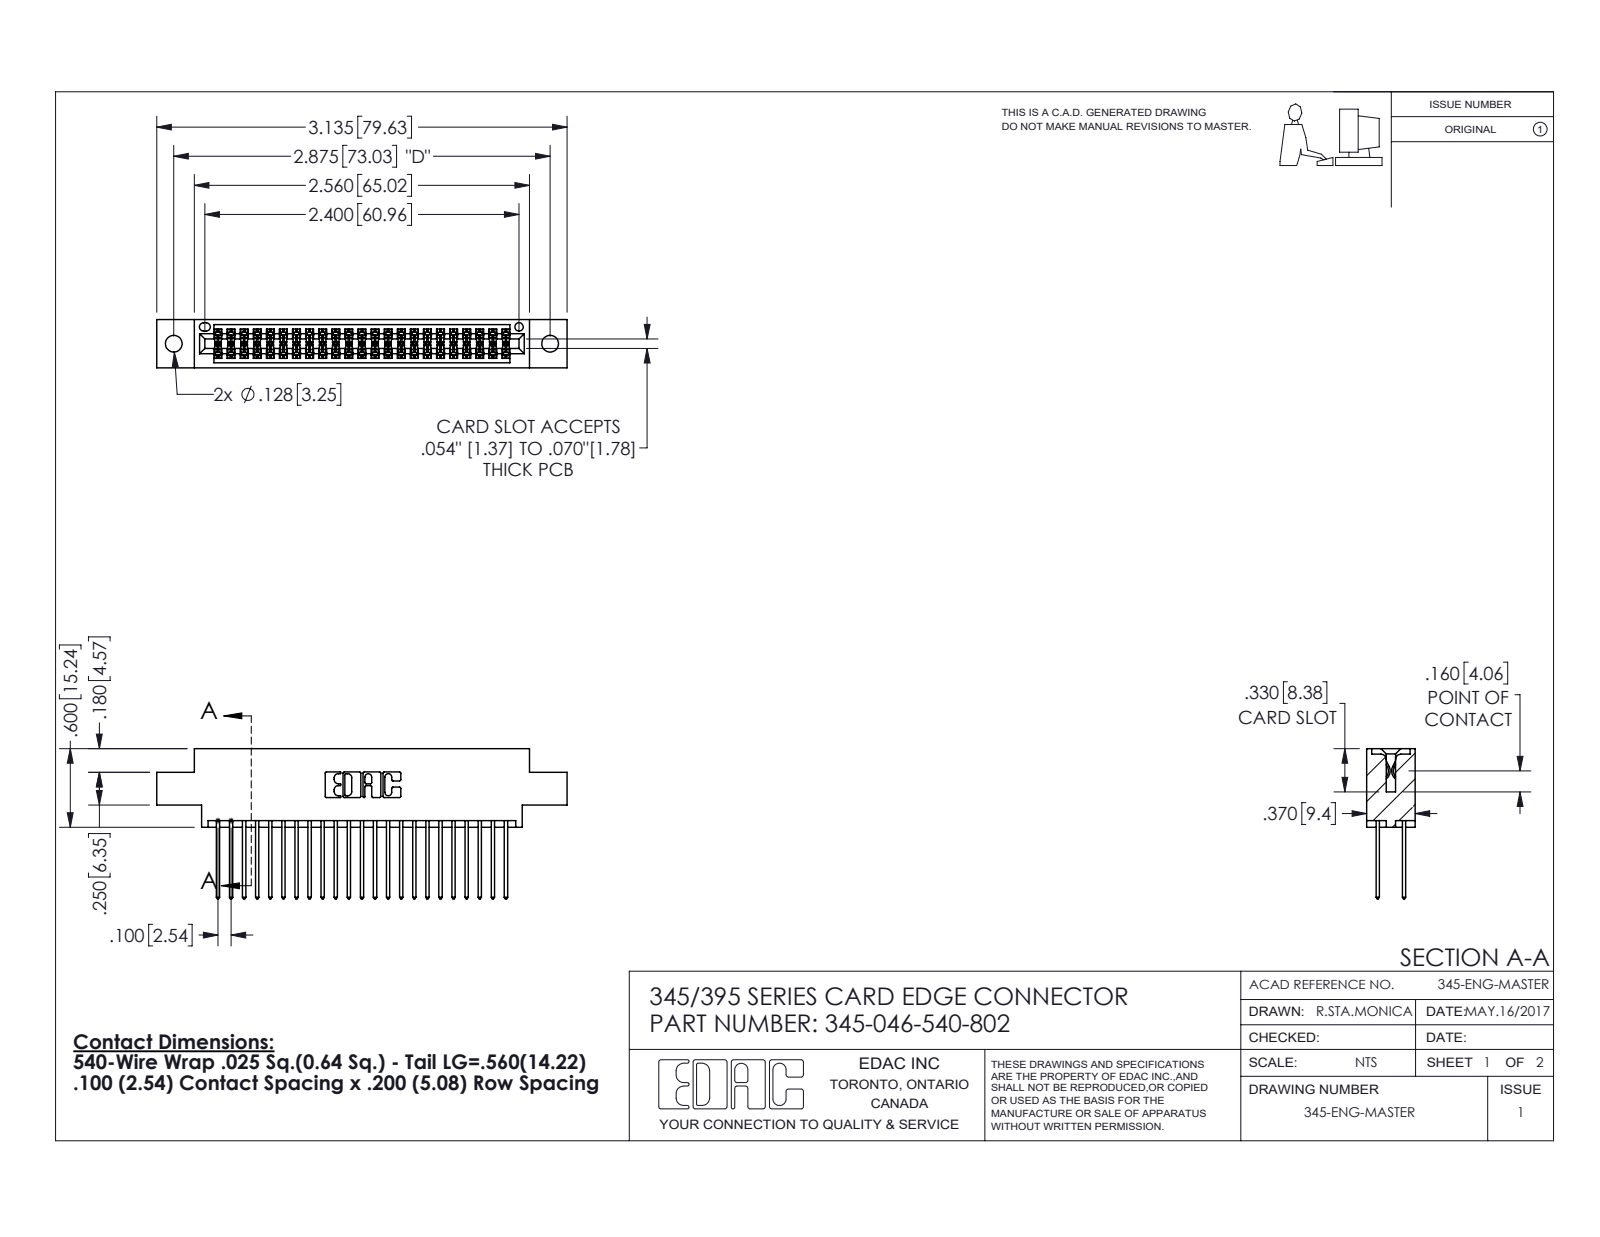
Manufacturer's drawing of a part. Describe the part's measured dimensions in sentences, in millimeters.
The part is named "345 Part_0.170 Offset - 0.128 Dia; 345-292-001_345-293-140; 345-046-540-802". Its 3-D file was written by "SolidWorks 2016 (CONFIG_CONTROL_DESIGN)". It is 47 solids with 2430 faces: 1602 planar, 828 cylindrical and 0 other. Overall it measures 79.6 by 29.1 by 9.4 millimeters. Its volume is 7 590 cubic millimeters and its surface area 11 520 square millimeters. Round holes: 2 of diameter 3.3, 1 of diameter 1.6. Partial cylindrical surfaces (rounded edges, fillets, slot ends): 69 of radius 0.2, 46 of radius 0.3, 22 of radius 0.3, 6 of radius 0.2, 6 of radius 0.8, 3 of radius 0.7, 2 of radius 0.4, 2 of radius 0.5. The main face-to-face distances are 7.6, 1.8, 5.1, 2.5, 6.9, 0.6, 9.4, 5.7, 4.4, 3.8. The hole center spacings are 6.9, 67.1, 73.
